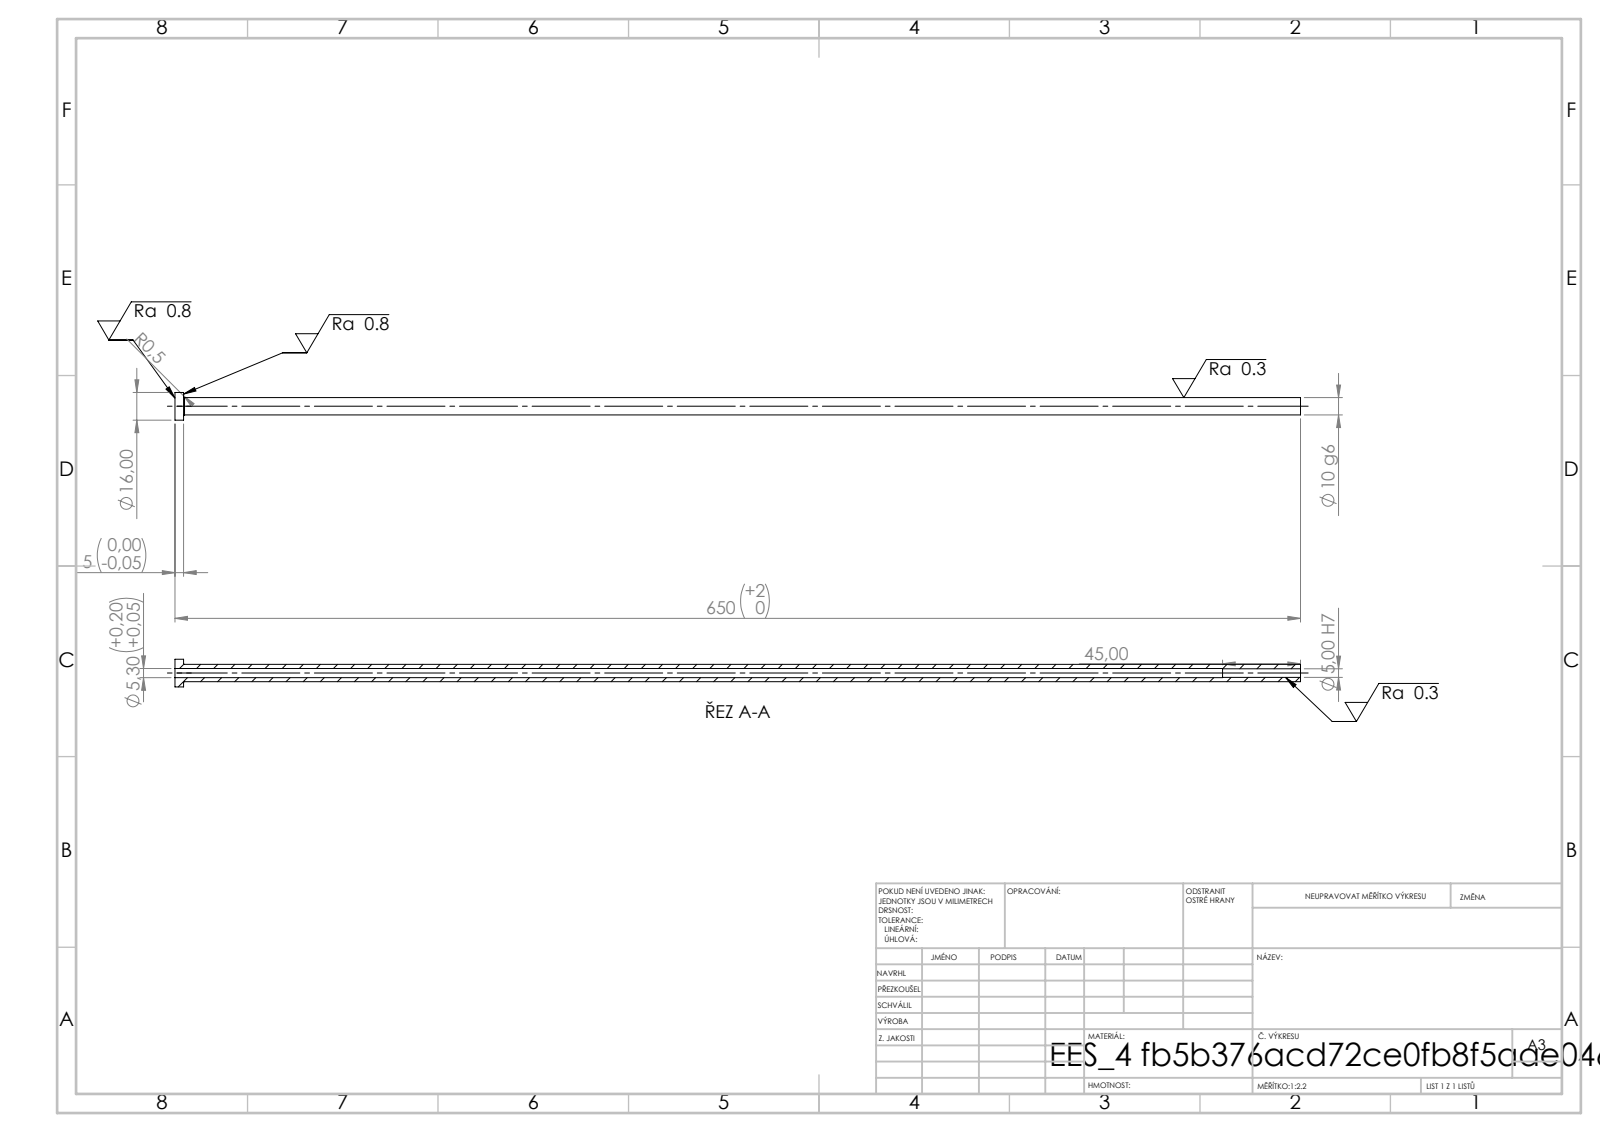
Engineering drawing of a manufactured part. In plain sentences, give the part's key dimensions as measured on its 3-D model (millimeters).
Its 3-D file was written by "SolidWorks 2019 (CONFIG_CONTROL_DESIGN)". It is 1 solid with 14 faces: 4 planar, 8 cylindrical and 2 other. Overall it measures 650 by 16 by 16 millimeters. Its volume is 37 434 cubic millimeters and its surface area 31 651 square millimeters. Round holes: 1 of diameter 5, 1 of diameter 5.3. Round bosses or shafts: 1 of diameter 16, 1 of diameter 10. The main face-to-face distances are 5, 650, 645, 605, 600, 45.
